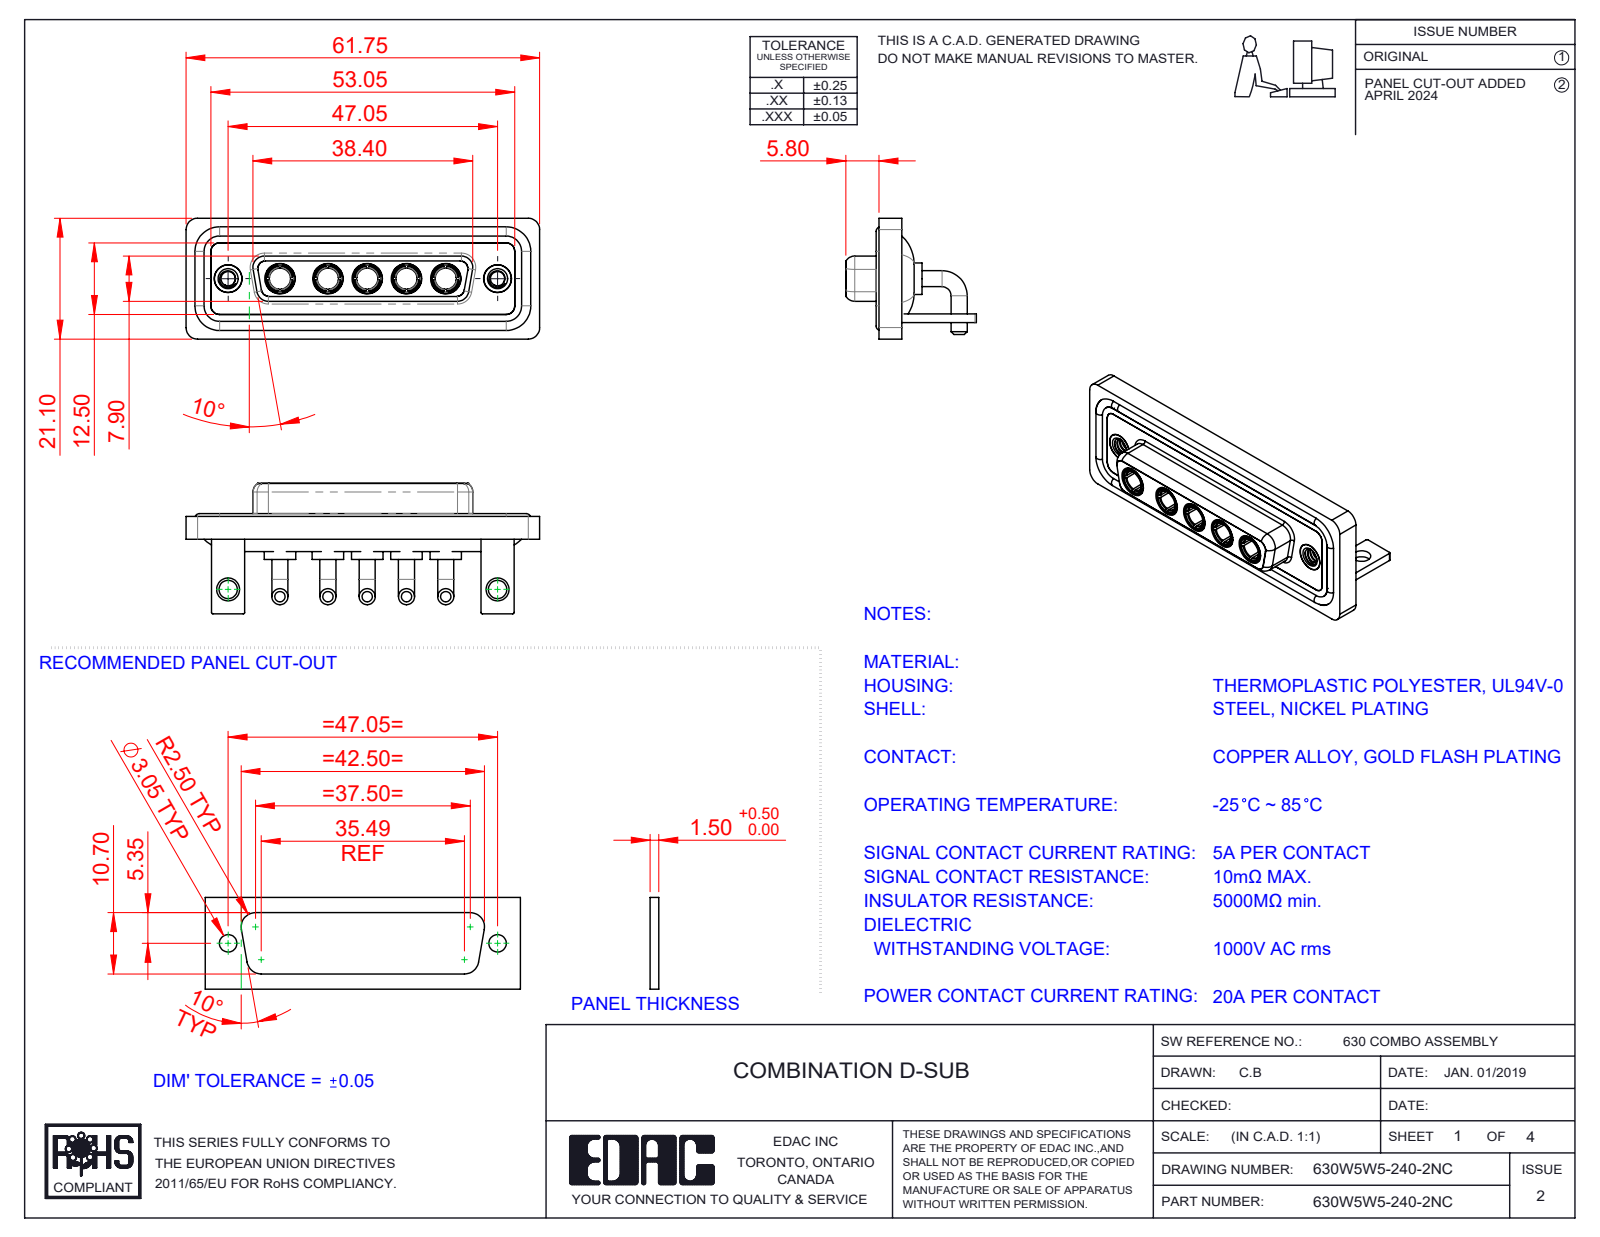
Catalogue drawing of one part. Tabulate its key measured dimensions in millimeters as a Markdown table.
| quantity | value |
| --- | --- |
| part name | Power Socket_20A RA; 630Combo Stabilizer Bracket_50 Contacts; 630Combo Shell Rear_25 Contacts; 630Combo Waterproof Housing_25 Contacts (+4 more) |
| STEP written by | SolidWorks 2023 (CONFIG_CONTROL_DESIGN) |
| units | millimeters |
| bodies | 19 solids, 818 faces (270 planar, 335 cylindrical, 213 other) |
| overall size | 61.75 × 22.8 × 21.1 |
| volume | 8 794 mm³ |
| surface area | 14 552 mm² |
| round holes (diameter × count) | 4.85 × 7, 3.7 × 5, 5.3 × 5, 2.5 × 2, 3.2 × 2, 4 × 2, 4.05 × 2, 5 × 2 |
| round bosses / shafts (diameter × count) | 2.8 × 10, 5.5 × 5, 5.2 × 5, 4.96 × 5, 4.75 × 5, 3.75 × 5, 1.6 × 4, 4.95 × 2 |
| partial cylindrical surfaces (radius × count) | 2 × 19, 1.5 × 18, 0.25 × 16, 1.35 × 8, 1.6 × 8, 0.5 × 5, 2.1 × 5, 0.6 × 4 |
| main face-to-face distances | 0.4, 1.8, 2.9, 3.7, 1.5, 4.1, 1.1, 1.4, 1.6, 2.5 |
| hole center spacings | 6.86, 9.04, 38.01, 47.05, 6.87, 8.38, 13.72, 13.73 |
